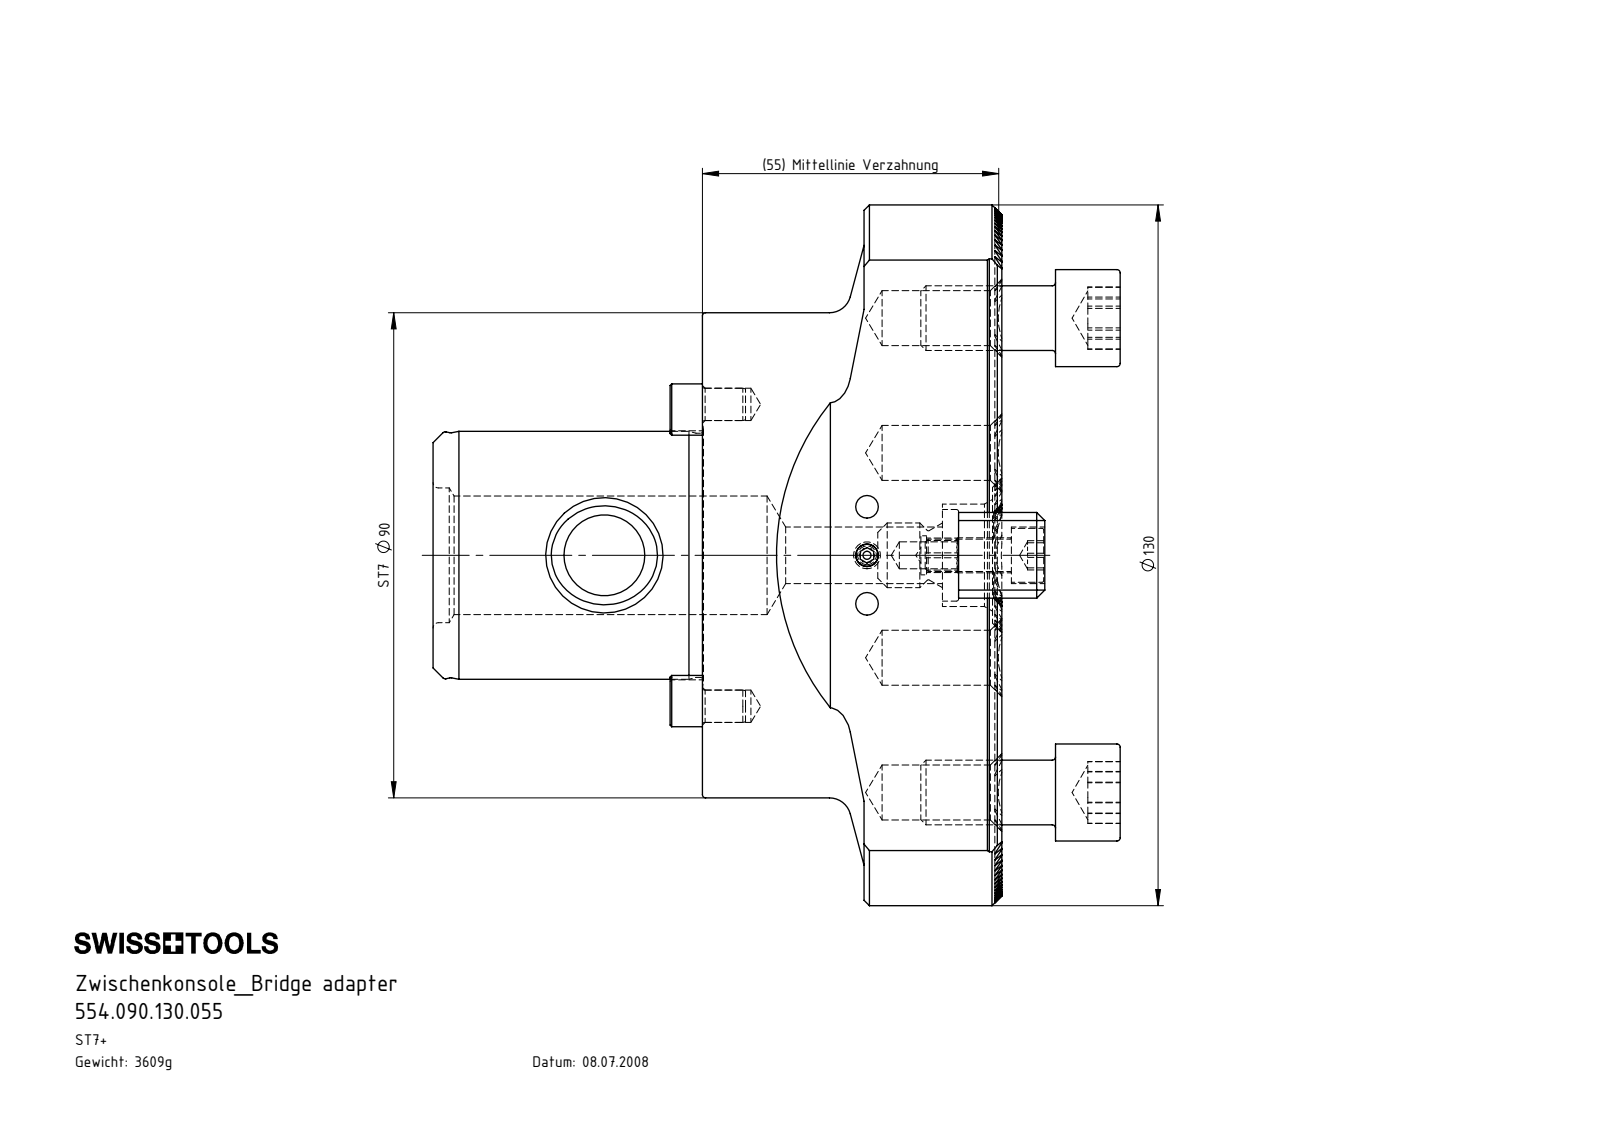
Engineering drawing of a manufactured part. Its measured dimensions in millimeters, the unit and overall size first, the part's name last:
Units: millimetres
Overall size (bounding box): 130 × 127.54 × 90
Round holes (diameter × count): ⌀10.2 ×8, ⌀4.2 ×3, ⌀6 ×2, ⌀10.5 ×2, ⌀1.5 ×1, ⌀5 ×1, ⌀6.5 ×1, ⌀7.24 ×1, ⌀15 ×1, ⌀19 ×1, ⌀22 ×1, ⌀25 ×1
Round bosses / shafts (diameter × count): ⌀12 ×5, ⌀18 ×4, ⌀90 ×1, ⌀46 ×1, ⌀45.8 ×1, ⌀45.3 ×1, ⌀17 ×1, ⌀10 ×1
Partial cylindrical surfaces — rounded edges, fillets, slot ends (radius × count): R0.14 ×34, R0.5 ×4, R6.97 ×2, R23.05 ×2, R7.95 ×1, R65 ×1
Main face-to-face distances: 1.73, 17.32, 70, 8.66, 3.46, 5.2, 6.93, 15.59, 19.05, 3.47
Hole centre spacings: 21.93, 25, 25.61, 27.59, 40, 47.17, 48.33, 51.08
Volume: 459 721 mm³ · Surface area: 74 723 mm²
Bodies: 12 solids, 888 faces (480 planar, 215 cylindrical, 193 other)
Part name (STEP PRODUCT): ST7-Ko1.K01.055; ST7-Ko1.K01.055_A; Ko1-ER1.001.016_A; ISO 4762 - M6 x 16 (+4 more)
STEP written by: SolidWorks 2015 (CONFIG_CONTROL_DESIGN)
